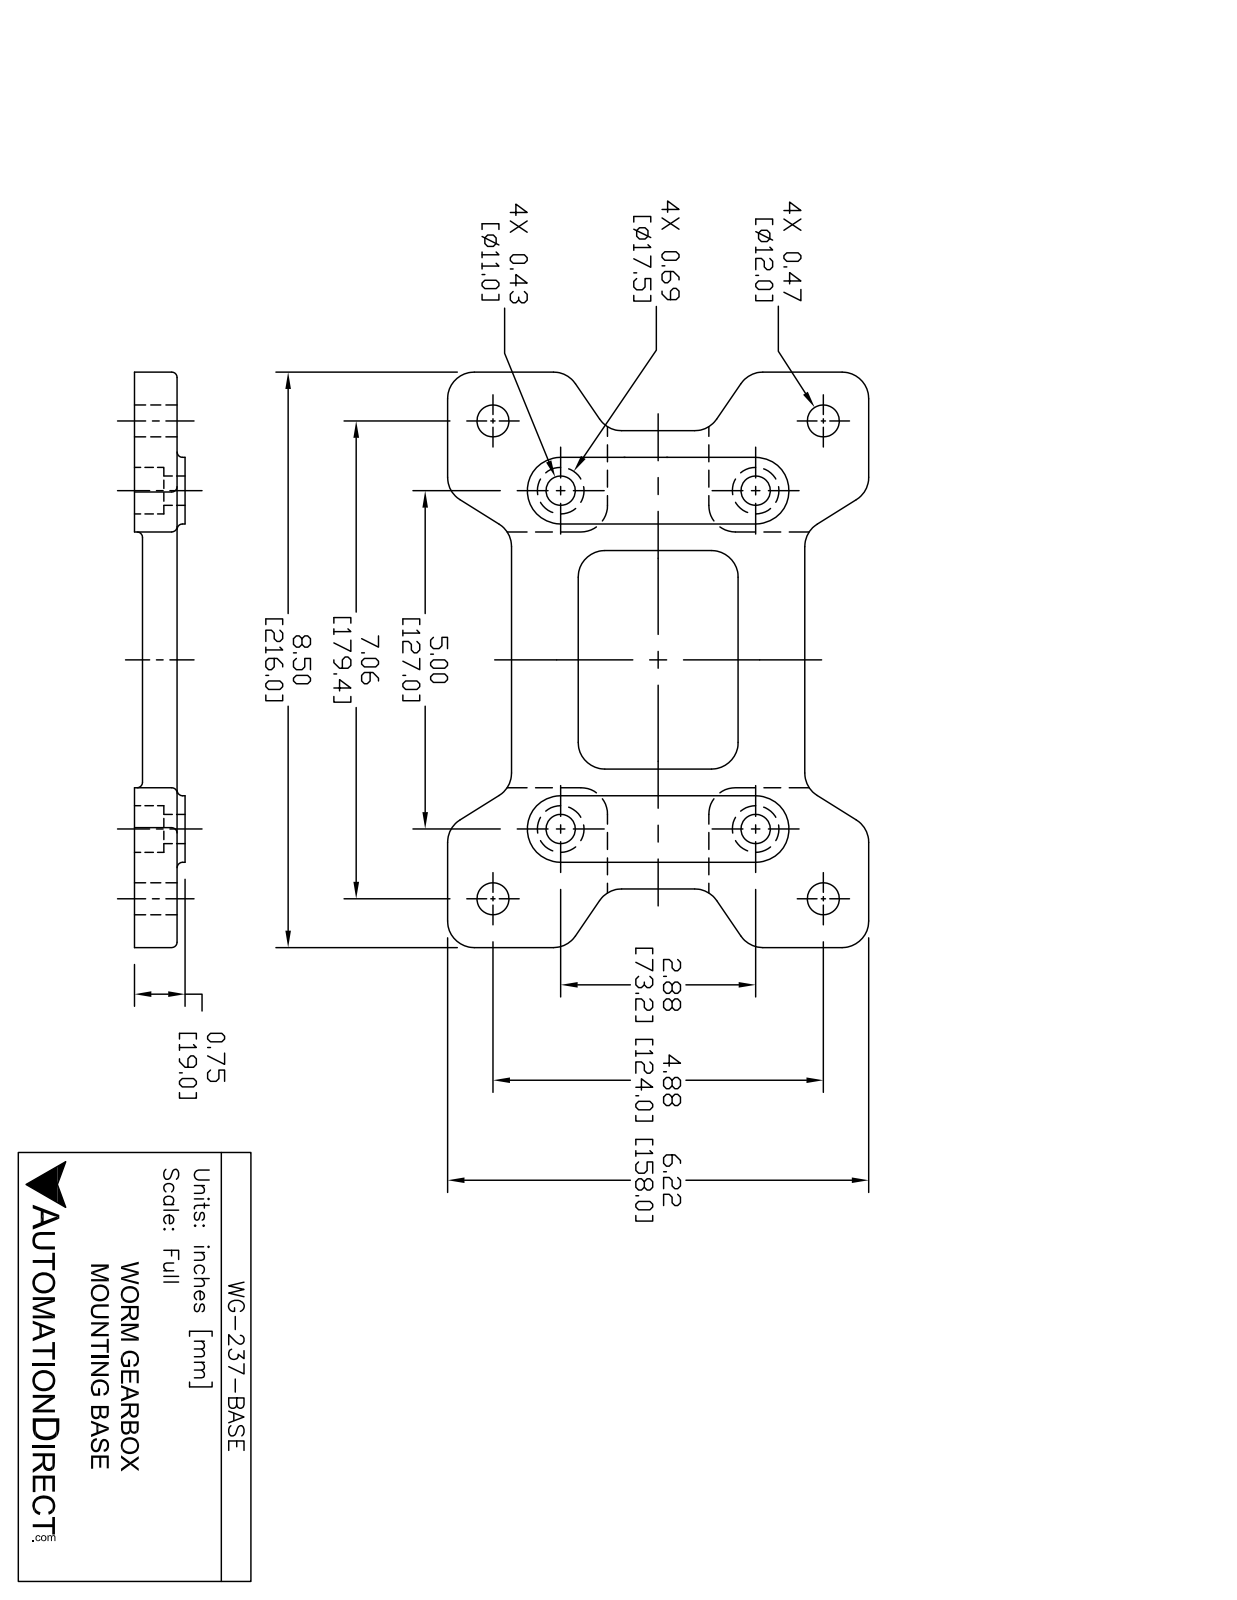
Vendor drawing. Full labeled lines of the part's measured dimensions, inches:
Part name (STEP PRODUCT): WG-237-BASE
STEP written by: SolidWorks 2017 (AUTOMOTIVE_DESIGN)
Units: inches
Bodies: 1 solid, 128 faces (48 planar, 70 cylindrical, 10 other)
Overall size (bounding box): 8.504 × 6.22 × 0.748
Volume: 19.05 in³ · Surface area: 100.6 in²
Round holes (diameter × count): ⌀0.433 ×4, ⌀0.472 ×4, ⌀0.689 ×4
Partial cylindrical surfaces — rounded edges, fillets, slot ends (radius × count): R0.394 ×24, R0.039 ×4, R0.079 ×4, R0.315 ×4, R0.492 ×4
Main face-to-face distances: 0.63, 0.118, 0.512, 0.748, 5.276, 0.984, 0.945, 1.929, 4.291, 3.346
Hole centre spacings: 1.437, 4.017, 6.114, 7.173, 2.882, 4.882, 5, 5.771
